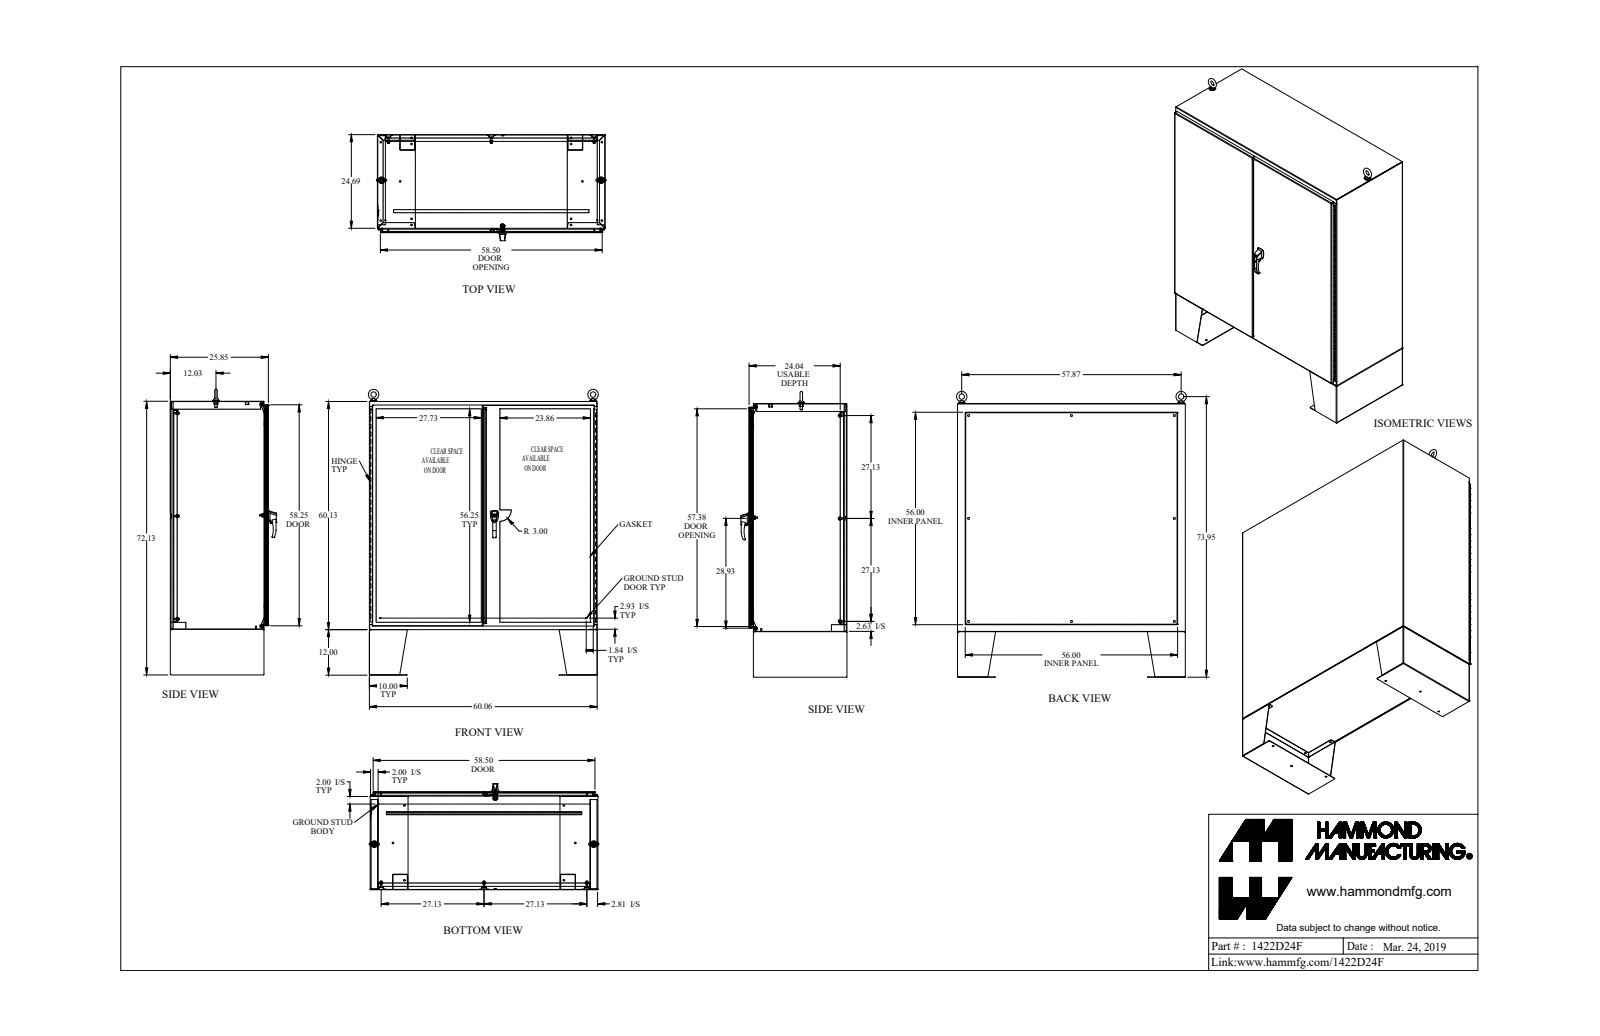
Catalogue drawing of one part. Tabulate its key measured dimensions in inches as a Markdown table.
| quantity | value |
| --- | --- |
| part name | 1422D24F_Default |
| STEP written by | SolidWorks 2019 (CONFIG_CONTROL_DESIGN) |
| units | inches |
| bodies | 90 solids, 2769 faces (1280 planar, 1242 cylindrical, 247 other) |
| overall size | 75.778 × 61.121 × 27.963 |
| volume | 2 043 in³ |
| surface area | 40 891 in² |
| round holes (diameter × count) | 0.304 × 20, 0.437 × 14, 0.307 × 9, 0.563 × 8, 0.445 × 6, 0.11 × 2, 0.25 × 2, 0.257 × 2, 0.28 × 2, 0.281 × 2, 0.313 × 2, 0.39 × 2 |
| round bosses / shafts (diameter × count) | 1 × 10, 0.65 × 8, 0.375 × 8, 0.33 × 8, 0.281 × 6, 0.25 × 4, 1.75 × 2, 1.5 × 2 |
| partial cylindrical surfaces (radius × count) | 0.048 × 32, 0.143 × 32, 0.125 × 22, 0.018 × 16, 0.06 × 14, 0.116 × 12, 0.188 × 10, 0.05 × 8 |
| main face-to-face distances | 0.095, 0.095, 25.658, 25.753, 59.968, 25.753, 25.848, 0.125, 24.066, 23.971 |
| hole center spacings | 6, 58.7, 12, 59.613, 18, 61.104, 24, 63.132 |
